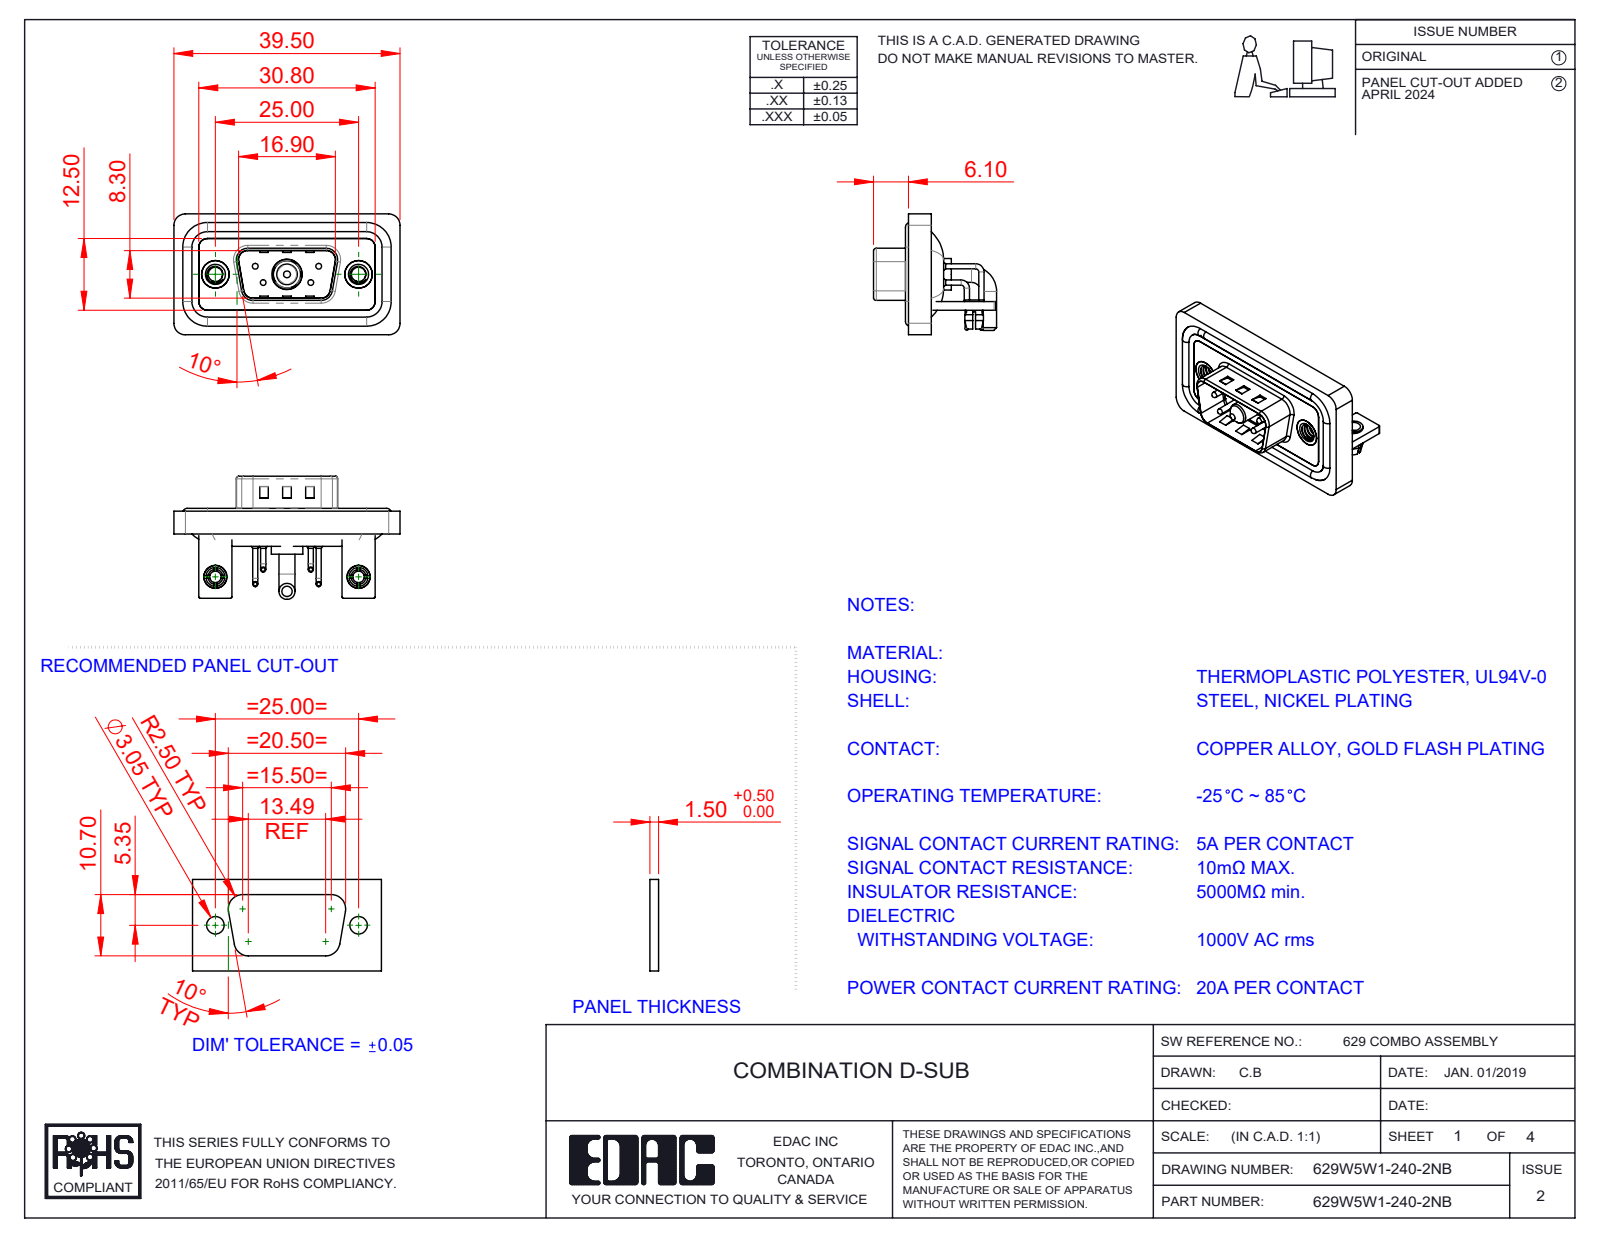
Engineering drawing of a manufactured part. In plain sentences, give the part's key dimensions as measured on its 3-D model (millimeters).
The part is named "629Combo Contact Row 2; 629Combo Shell Rear_09 Contacts; Power Pin_20A RA; 629Combo Housing_5W1 (+7 more)". Its 3-D file was written by "SolidWorks 2023 (CONFIG_CONTROL_DESIGN)". It is 17 solids with 1024 faces: 479 planar, 395 cylindrical and 150 other. Overall it measures 39.5 by 21.5 by 21.1 millimeters. Its volume is 4 784 cubic millimeters and its surface area 7 962 square millimeters. Round holes: 6 of diameter 2, 4 of diameter 0.75, 4 of diameter 1.6, 4 of diameter 2.5, 2 of diameter 3.2, 2 of diameter 4, 2 of diameter 4.8, 2 of diameter 5, 1 of diameter 4.85, 1 of diameter 5.3. Round bosses or shafts: 8 of diameter 0.9, 4 of diameter 1.6, 4 of diameter 1.5, 4 of diameter 1, 4 of diameter 0.65, 2 of diameter 4.9, 2 of diameter 4, 2 of diameter 3.4. Partial cylindrical surfaces (rounded edges, fillets, slot ends): 19 of radius 2, 18 of radius 1.5, 16 of radius 0.25, 9 of radius 0.5, 8 of radius 1.6, 4 of radius 0.6, 4 of radius 0.65, 4 of radius 0.9. The main face-to-face distances are 0.4, 1.5, 0.8, 2.9, 1.1, 2.1, 1.2, 1.6, 2.5, 3.7. The hole center spacings are 3.16, 5.72, 7.1, 12.5, 18.1, 25, 4.39, 4.4.
